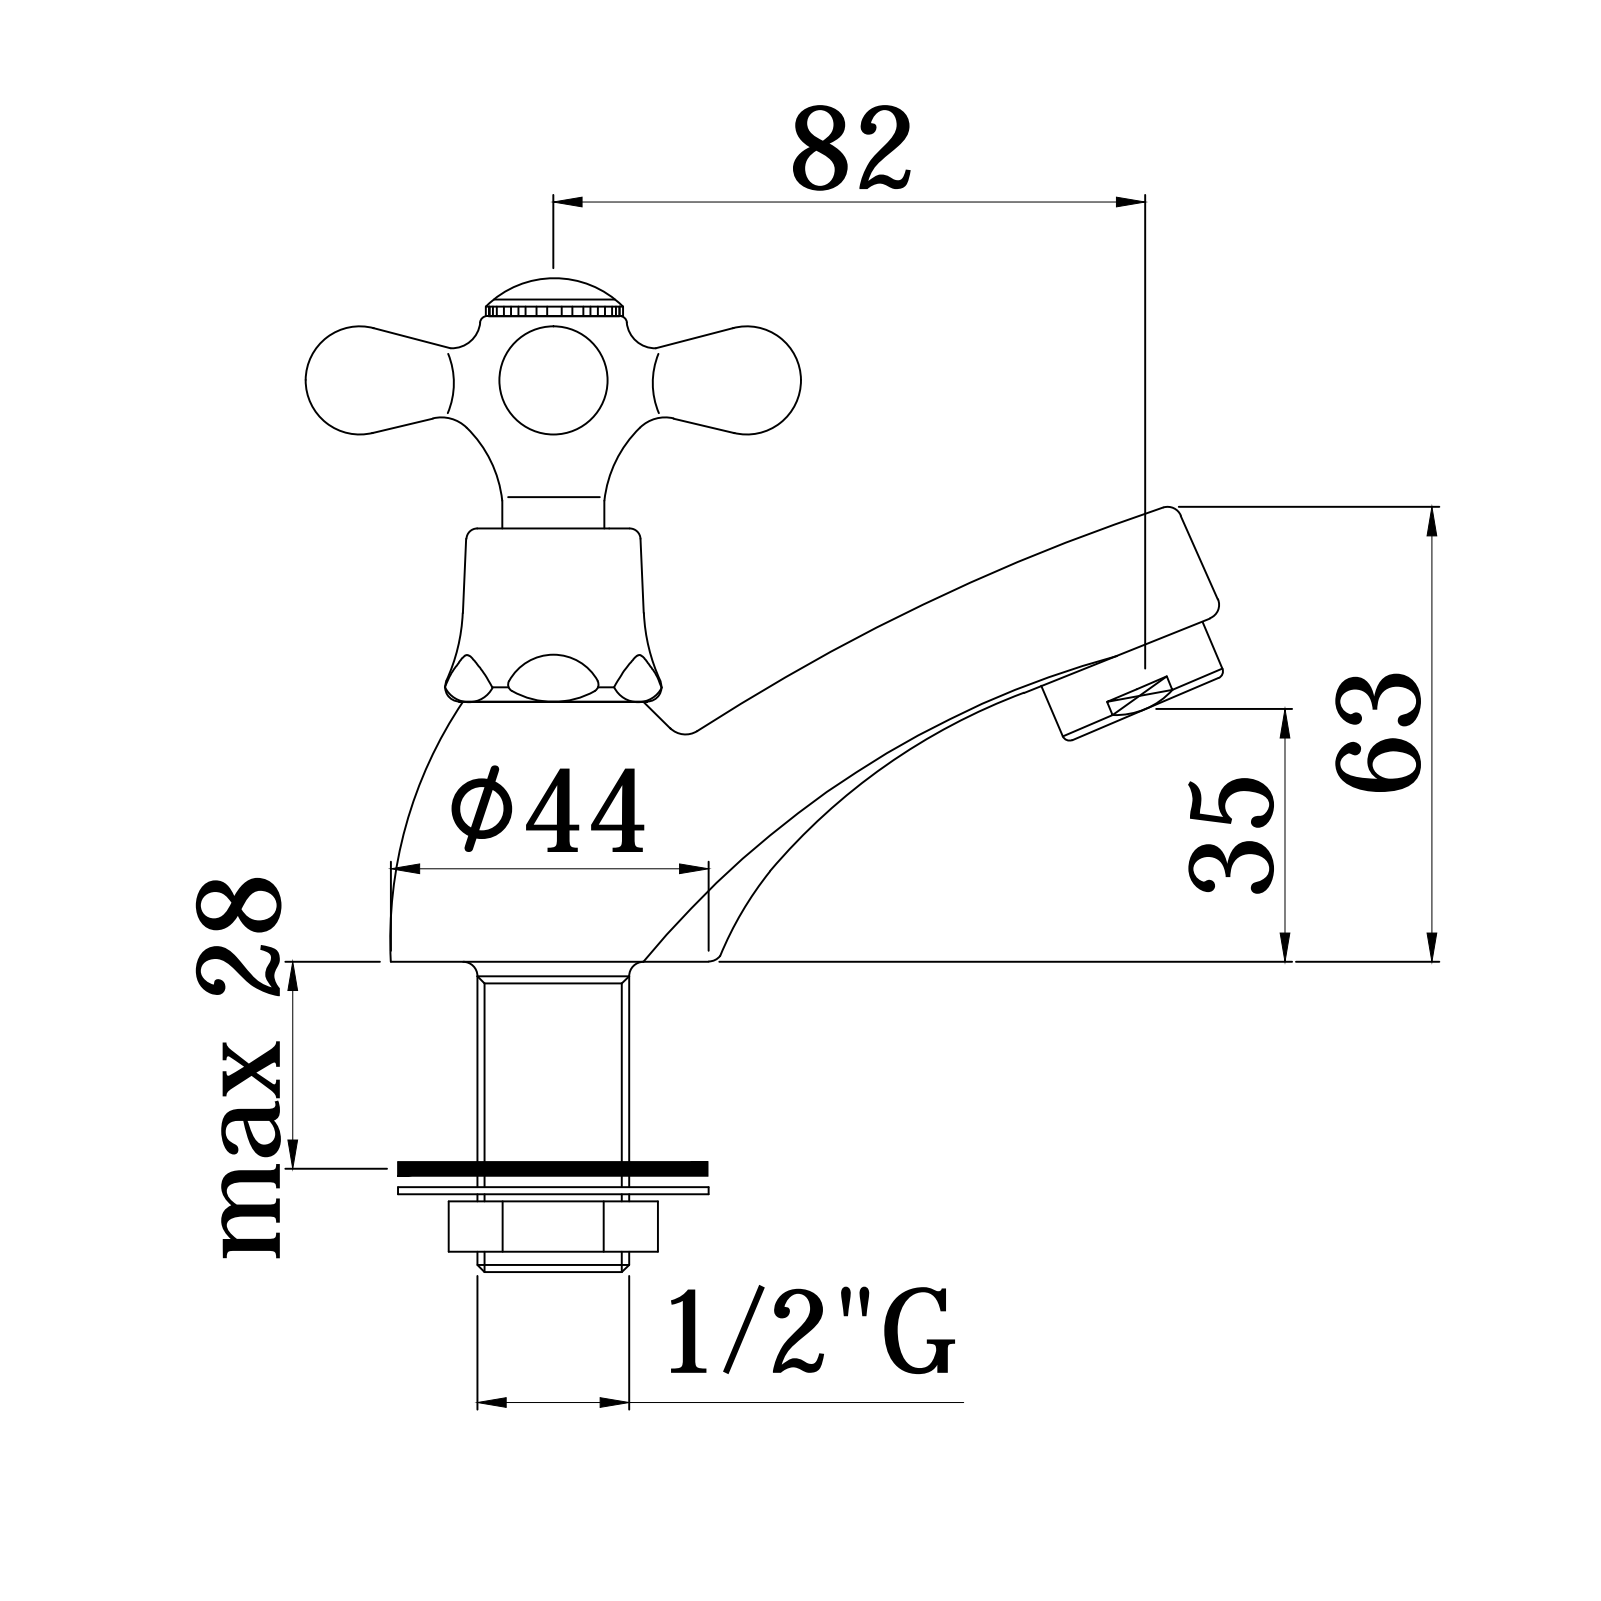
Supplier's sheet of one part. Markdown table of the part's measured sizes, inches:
| quantity | value |
| --- | --- |
| part name | IRV090CR |
| STEP written by | CREO PARAMETRIC BY PTC INC, 2020044 (CONFIG_CONTROL_DESIGN) |
| units | inches |
| bodies | 1 solid, 108 faces (28 planar, 15 cylindrical, 65 other) |
| overall size | 5.113 × 3.768 × 2.835 |
| volume | 7.579 in³ |
| surface area | 33.78 in² |
| round bosses / shafts (diameter × count) | 0.945 × 1, 0.709 × 1, 0.531 × 1 |
| partial cylindrical surfaces (radius × count) | 0.571 × 1, 0.591 × 1, 38.569 × 1, 39.199 × 1 |
| main face-to-face distances | 1.181, 1.043, 2.402, 0.157, 1.024, 1.457, 0.945, 0.866, 0.118, 3.63 |
